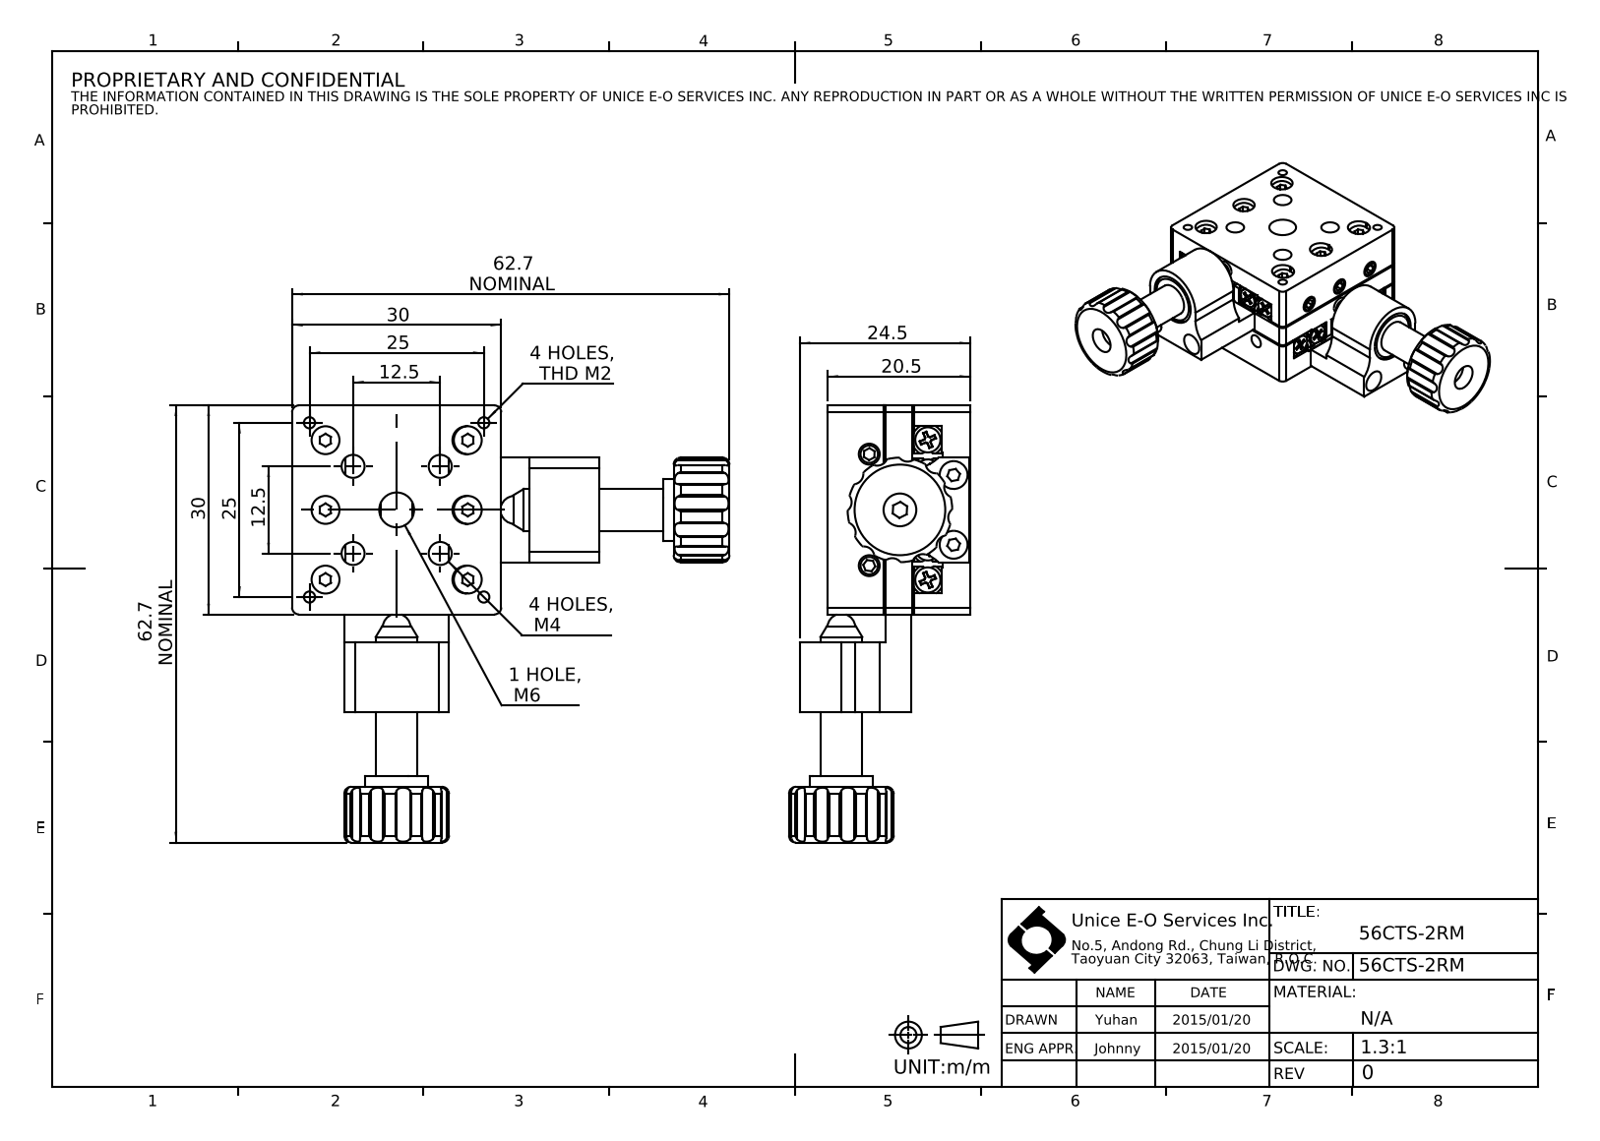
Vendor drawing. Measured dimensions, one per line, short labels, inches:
name: 56CTS-2RM
written by: SolidWorks 2016 (CONFIG_CONTROL_DESIGN)
unit: in
bodies: 65 solids, 1652 faces (803 planar, 595 cylindrical, 254 other)
size: 2.47 × 2.47 × 1.024
volume: 1.372 in³; area: 39.16 in²
holes: 44× ⌀0.063, 24× ⌀0.157, 12× ⌀0.094, 11× ⌀0.098, 4× ⌀0.083, 4× ⌀0.13, 3× ⌀0.102, 3× ⌀0.165, 2× ⌀0.118, 2× ⌀0.185, 2× ⌀0.232, 2× ⌀0.236
bosses: 20× ⌀0.079, 10× ⌀0.157, 8× ⌀0.142, 8× ⌀0.077, 6× ⌀0.118, 2× ⌀0.354
rounds: 48× R0.012, 24× R0.059, 11× R0.049, 5× R0.079, 4× R0.039, 4× R0.197, 2× R0.236, 2× R0.295
face distances: 0.327, 0.319, 0.161, 0.154, 0.165, 0.157, 0.335, 0.488, 0.173, 0.61
hole spacings: 0.394, 0.61, 0.439, 0.193, 0.348, 0.726, 0.741, 0.778
